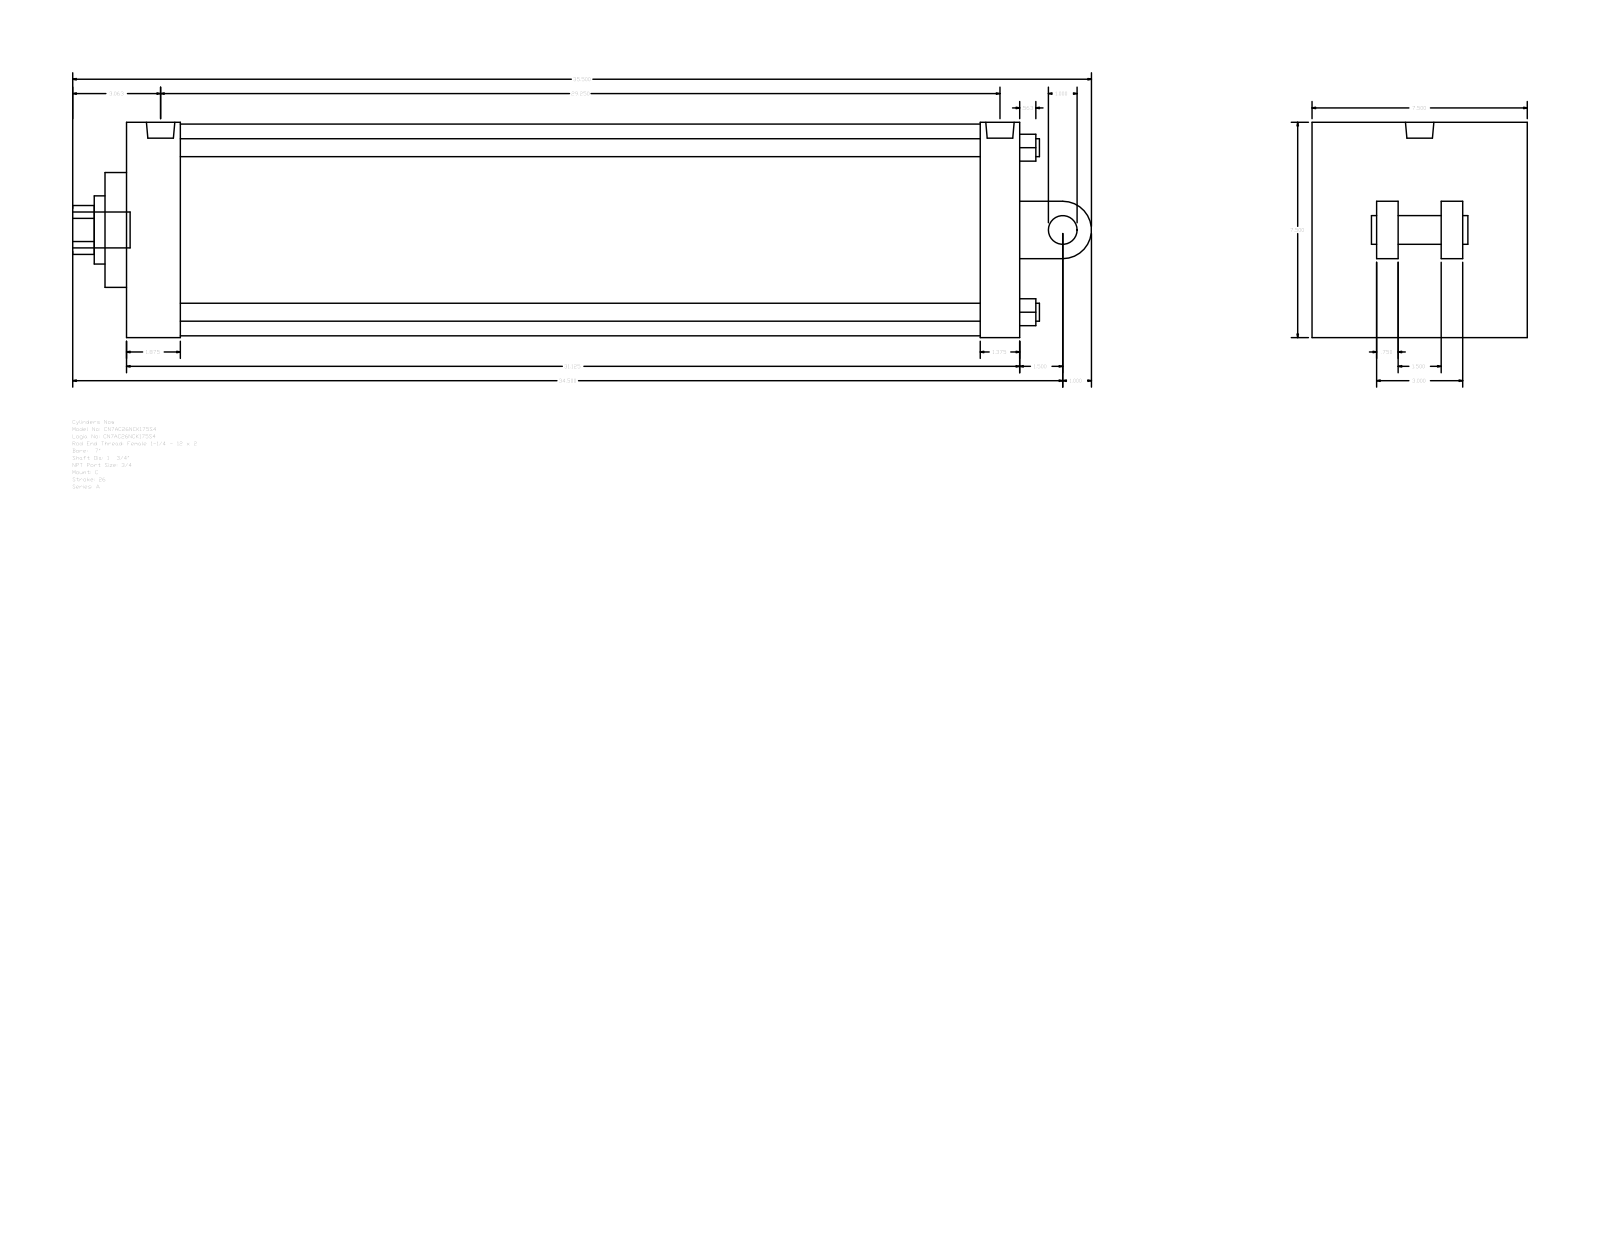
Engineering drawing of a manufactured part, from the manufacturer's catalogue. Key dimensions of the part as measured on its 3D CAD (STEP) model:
Part name (STEP PRODUCT): A_C__0700_1.75
STEP written by: GSSL Pune (CONFIG_CONTROL_DESIGN)
Units: millimetres
Bodies: 0 solids, 104 faces (75 planar, 29 cylindrical, 0 other)
Overall size (bounding box): 901.7 × 190.5 × 190.5
Round holes (diameter × count): ⌀15.88 ×4, ⌀15.08 ×2, ⌀25.12 ×1, ⌀44.45 ×1, ⌀60.33 ×1, ⌀187.32 ×1
Round bosses / shafts (diameter × count): ⌀15.08 ×2, ⌀31.75 ×1, ⌀25.4 ×1, ⌀25.12 ×1
Partial cylindrical surfaces — rounded edges, fillets, slot ends (radius × count): R21.63 ×1, R25.4 ×1
Main face-to-face distances: 190.5, 790.58, 19.05, 76.2, 57.15, 44.45, 47.63, 742.95, 755.65, 708.02
Hole centre spacings: 102.91, 145.54, 205.82, 5.56
